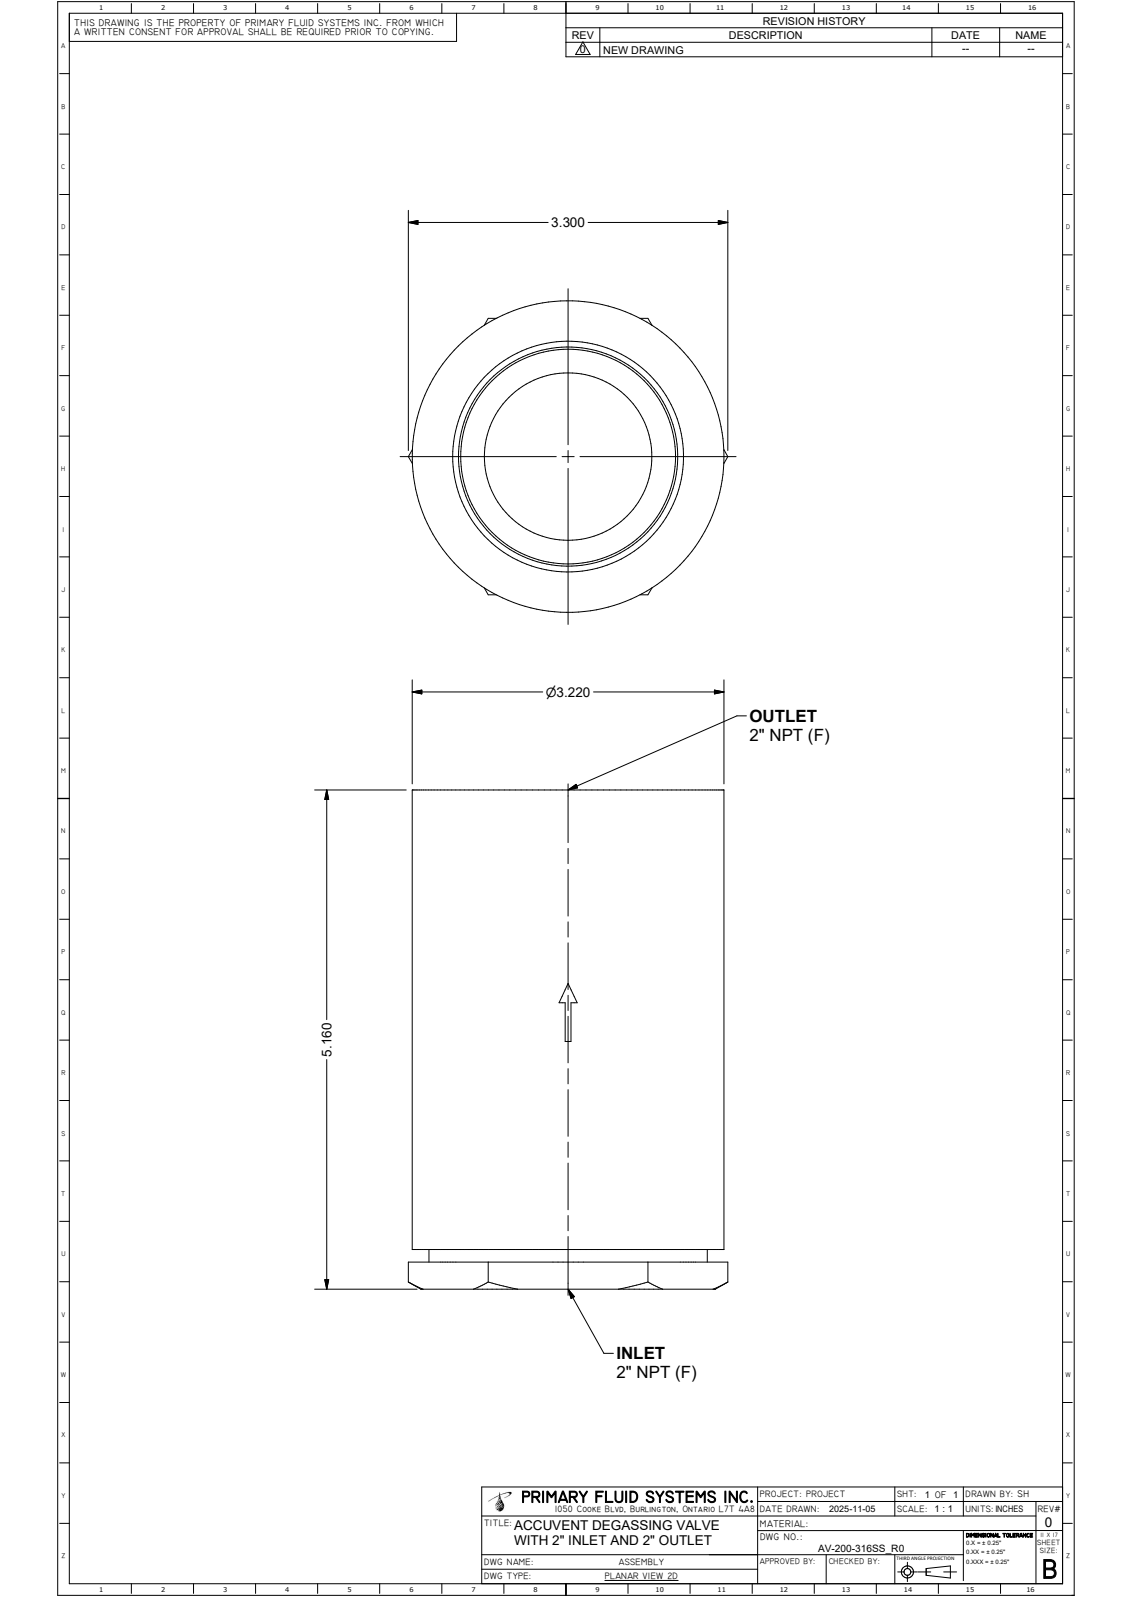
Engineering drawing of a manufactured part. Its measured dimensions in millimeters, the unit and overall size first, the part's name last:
Units: millimetres
Overall size (bounding box): 131.1 × 83.8 × 81.8
Round holes (diameter × count): ⌀43.9 ×1, ⌀56.4 ×1, ⌀62.7 ×1, ⌀63 ×1, ⌀74.9 ×1
Round bosses / shafts (diameter × count): ⌀81.8 ×1, ⌀73 ×1
Partial cylindrical surfaces — rounded edges, fillets, slot ends (radius × count): R40.8 ×1
Main face-to-face distances: 131.1, 111, 20.1, 10.4, 100.6, 120.7, 34.3, 23.9, 76.7, 96.8
Volume: 331 500 mm³ · Surface area: 77 610 mm²
Bodies: 2 solids, 55 faces (33 planar, 8 cylindrical, 14 other)
Part name (STEP PRODUCT): AV-200-316SS_R0; AV-1A-200NPT_R1; BUSHING_250X200_R0
STEP written by: Autodesk Inventor 2026 (AUTOMOTIVE_DESIGN)
